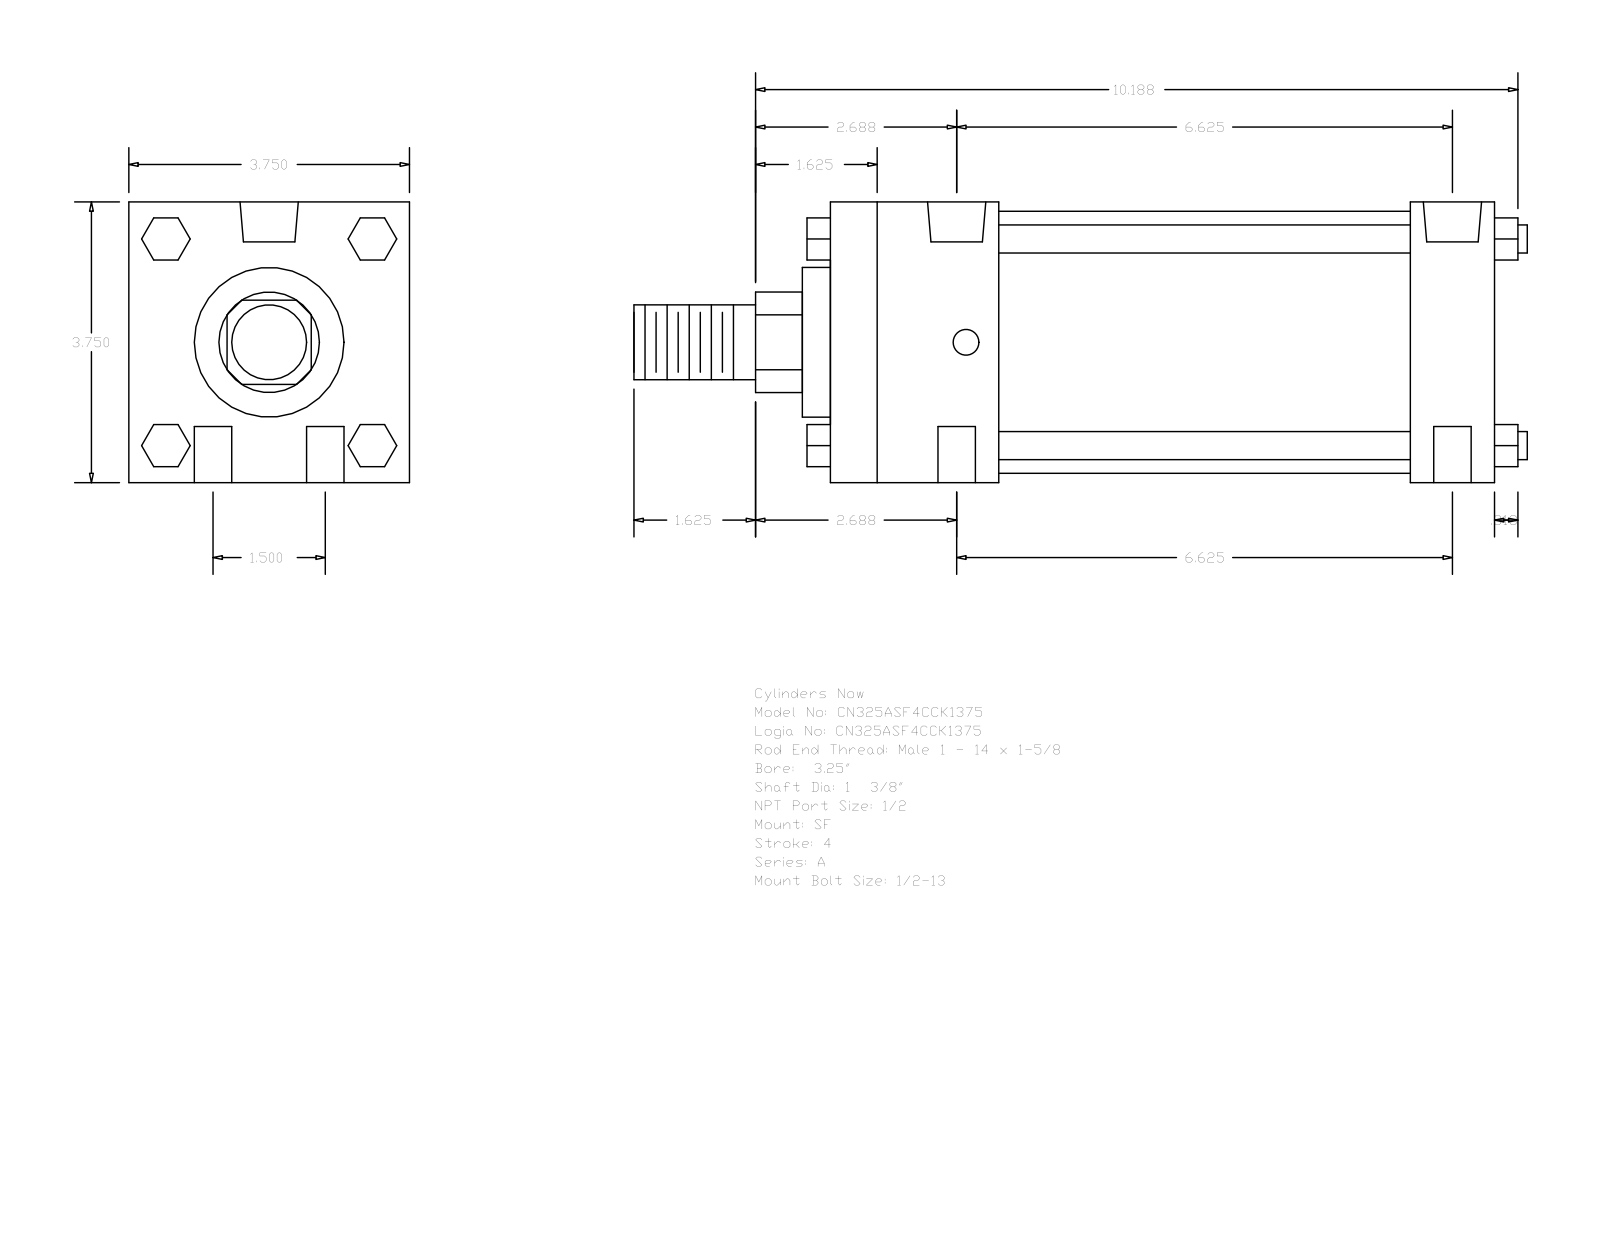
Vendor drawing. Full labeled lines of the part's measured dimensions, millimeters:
Part name (STEP PRODUCT): A_SF__0325_1.375
STEP written by: GSSL Pune (CONFIG_CONTROL_DESIGN)
Units: millimetres
Bodies: 0 solids, 124 faces (94 planar, 30 cylindrical, 0 other)
Overall size (bounding box): 303.21 × 95.25 × 95.25
Round holes (diameter × count): ⌀12.7 ×4, ⌀8.73 ×2, ⌀19.77 ×2
Round bosses / shafts (diameter × count): ⌀9.53 ×4, ⌀88.9 ×1, ⌀50.8 ×1, ⌀34.92 ×1, ⌀25.4 ×1
Partial cylindrical surfaces — rounded edges, fillets, slot ends (radius × count): R17.06 ×1
Main face-to-face distances: 95.24, 225.42, 57.15, 196.85, 28.57, 139.7, 168.27, 66.67, 9.52, 206.37
Hole centre spacings: 19.05, 169.35, 168.28, 38.1, 172.54, 161.92
